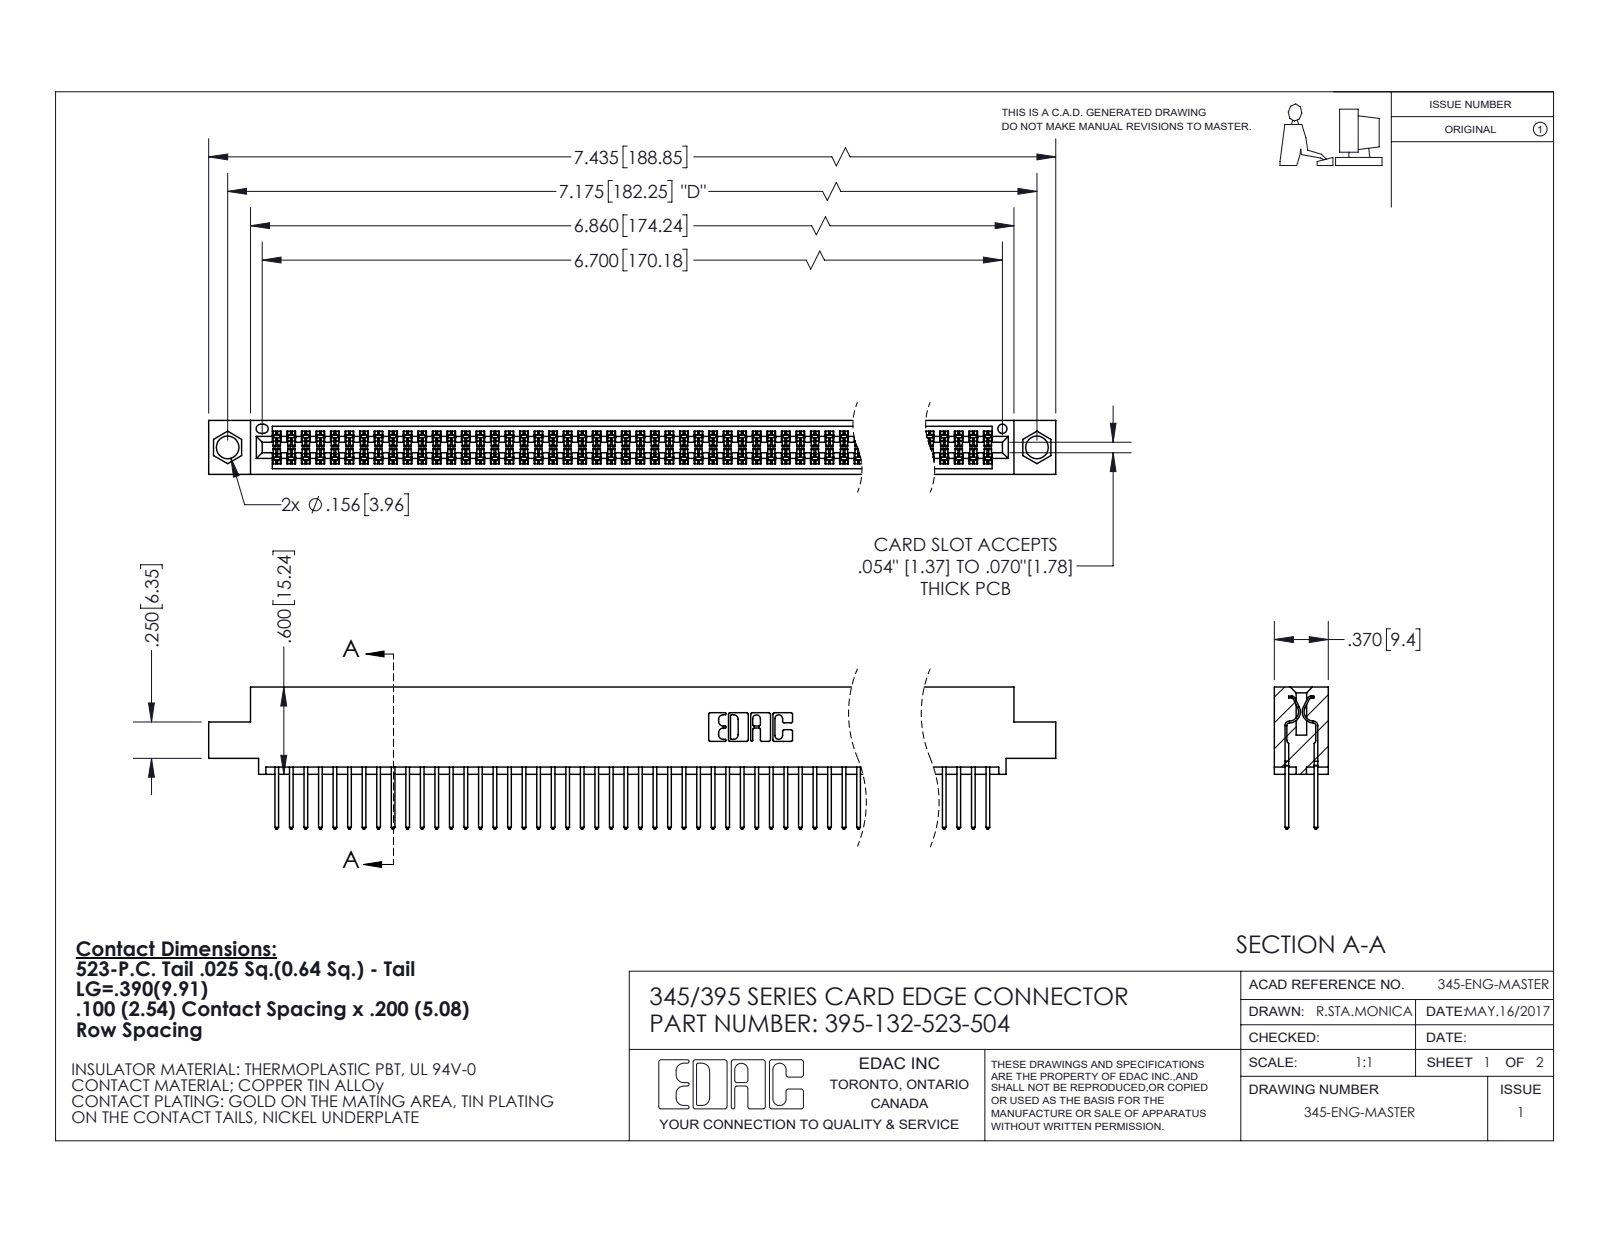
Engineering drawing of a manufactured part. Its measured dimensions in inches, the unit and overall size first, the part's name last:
Units: inches
Overall size (bounding box): 7.435 × 0.977 × 0.37
Round holes (diameter × count): ⌀0.156 ×2, ⌀0.064 ×1
Partial cylindrical surfaces — rounded edges, fillets, slot ends (radius × count): R0.006 ×198, R0.01 ×132, R0.01 ×22, R0.007 ×6, R0.031 ×6, R0.026 ×3, R0.014 ×2, R0.019 ×2
Main face-to-face distances: 0.072, 0.298, 0.2, 0.098, 0.272, 0.025, 0.37, 0.225, 0.175, 0.149
Hole centre spacings: 0.27, 6.939, 7.175
Volume: 1.139 in³ · Surface area: 45.27 in²
Bodies: 133 solids, 6744 faces (4454 planar, 2290 cylindrical, 0 other)
Part name (STEP PRODUCT): 345-292-001_345-293-123; 395-132-523-504; 345 Part_0.110 Offset - 0.156 Dia-TI
STEP written by: SolidWorks 2020 (CONFIG_CONTROL_DESIGN)
